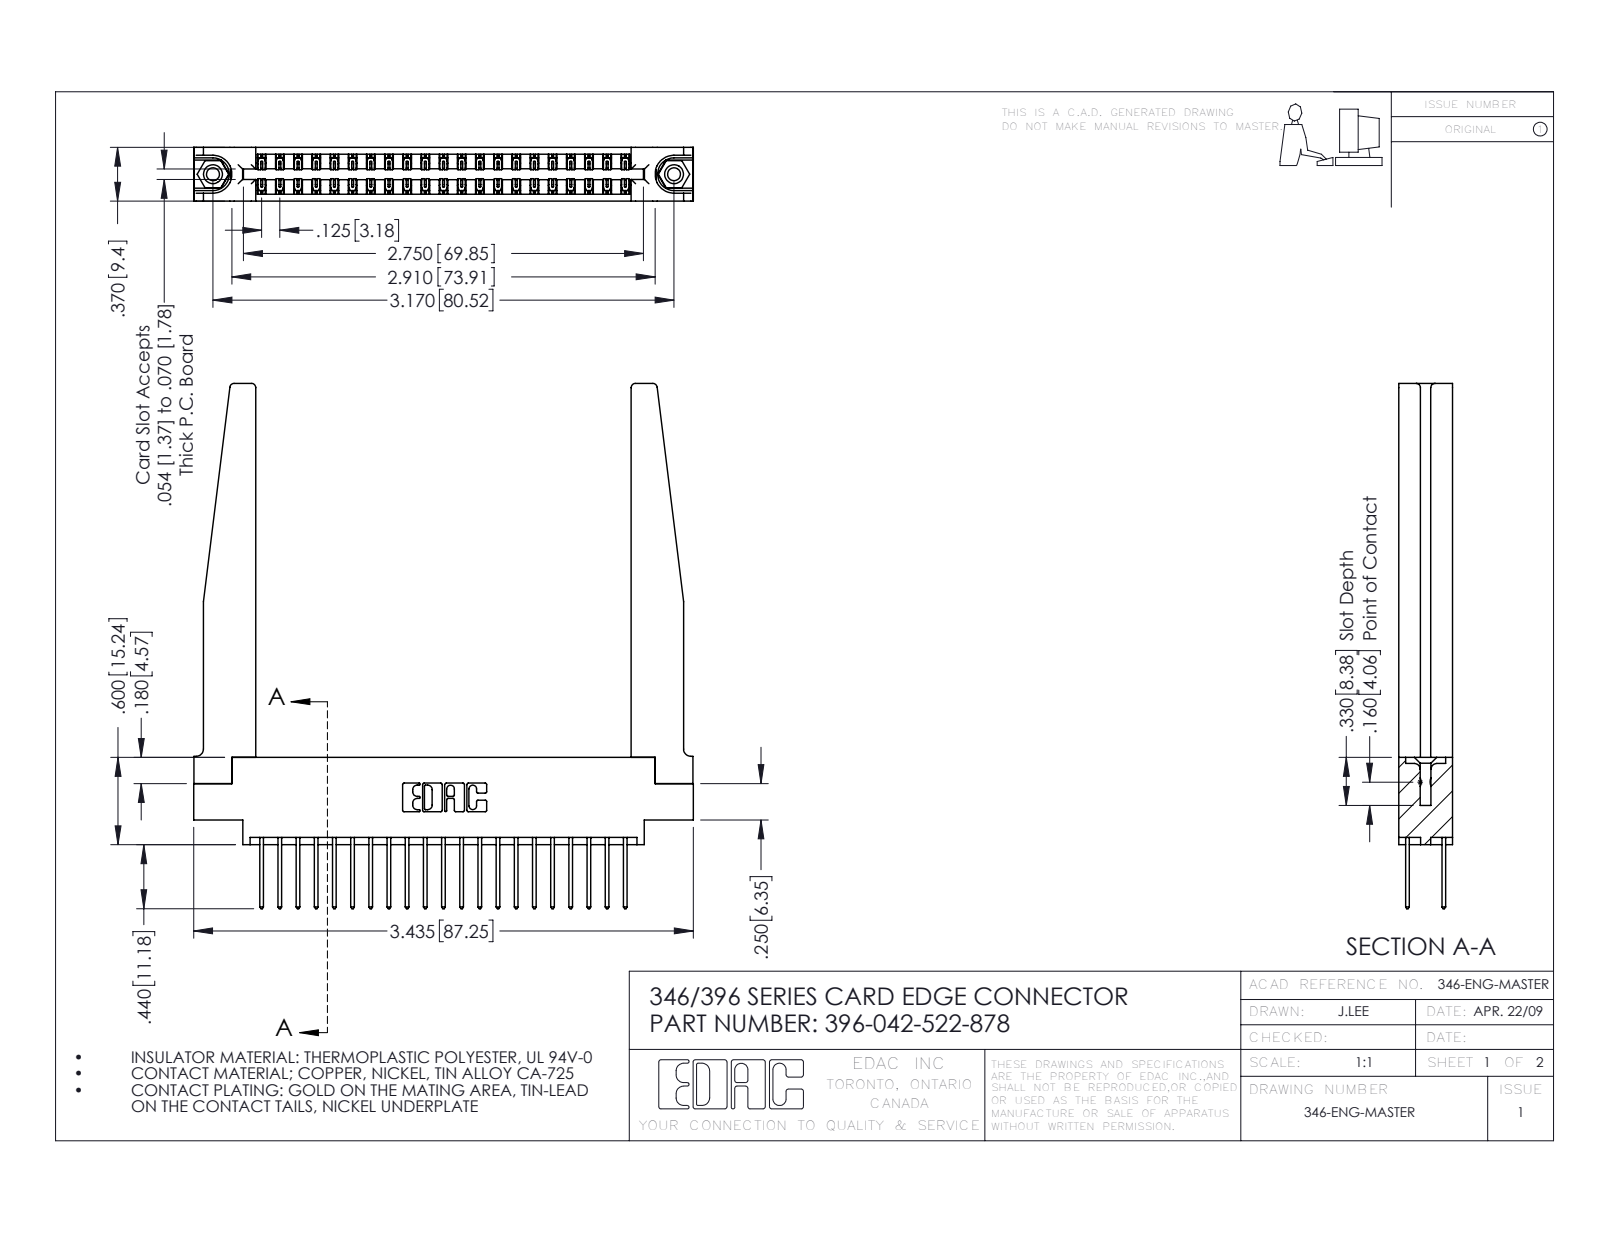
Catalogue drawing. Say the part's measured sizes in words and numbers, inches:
The part is named "345-292-001_345-293-122; 346-220-078_345-220-078; 345-250-001_345-250-001-102; 396-042-522-878 (+1 more)". Its 3-D file was written by "SolidWorks 2016 (CONFIG_CONTROL_DESIGN)". It is 47 solids with 2544 faces: 1692 planar, 800 cylindrical and 52 other. Overall it measures 3.61 by 3.435 by 0.37 inches. Its volume is 0.928 cubic inches and its surface area 28.35 square inches. Round holes: 2 of diameter 0.089, 2 of diameter 0.125, 2 of diameter 0.156, 1 of diameter 0.064. Round bosses or shafts: 2 of diameter 0.155. Partial cylindrical surfaces (rounded edges, fillets, slot ends): 63 of radius 0.006, 42 of radius 0.01, 22 of radius 0.01, 8 of radius 0.03, 6 of radius 0.007, 6 of radius 0.031, 3 of radius 0.026, 2 of radius 0.014. The main face-to-face distances are 0.37, 0.048, 0.322, 0.072, 0.25, 0.148, 0.15, 0.298, 0.025, 0.275. The hole center spacings are 0.246, 2.963, 3.17.
